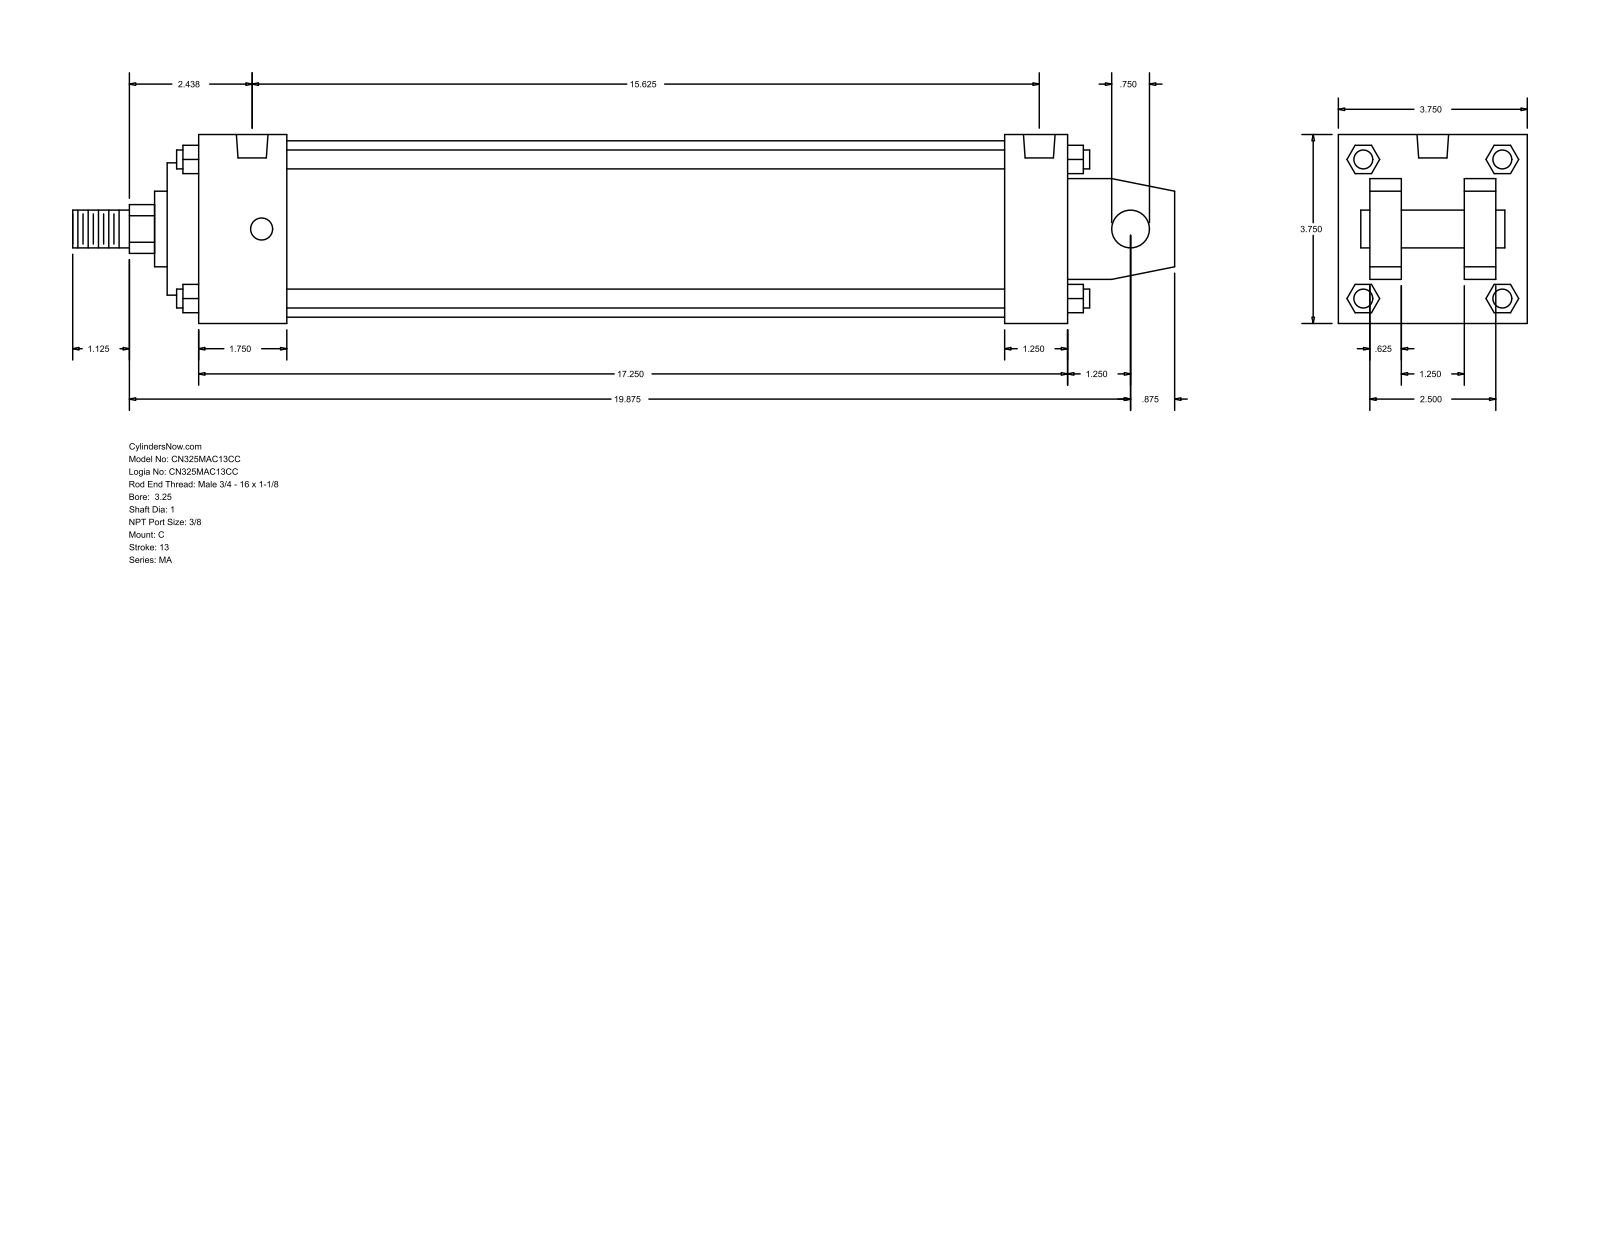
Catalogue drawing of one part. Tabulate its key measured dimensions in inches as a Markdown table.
| quantity | value |
| --- | --- |
| part name | MA_C__0325_1 |
| STEP written by | GSSL Pune (CONFIG_CONTROL_DESIGN) |
| units | inches |
| bodies | 0 solids, 141 faces (109 planar, 32 cylindrical, 0 other) |
| overall size | 21.875 × 3.75 × 3.75 |
| round holes (diameter × count) | 0.437 × 4, 0.627 × 2 |
| round bosses / shafts (diameter × count) | 0.375 × 4, 0.75 × 2, 3.5 × 1, 2.625 × 1, 1.5 × 1, 1 × 1 |
| partial cylindrical surfaces (radius × count) | 0.484 × 1 |
| main face-to-face distances | 3.75, 0.625, 2.5, 17.25, 1.25, 3.125, 1.875, 17.875, 16, 1.25 |
| hole center spacings | 15.25, 0.187, 0.188, 15.437, 15.438, 15.625 |
